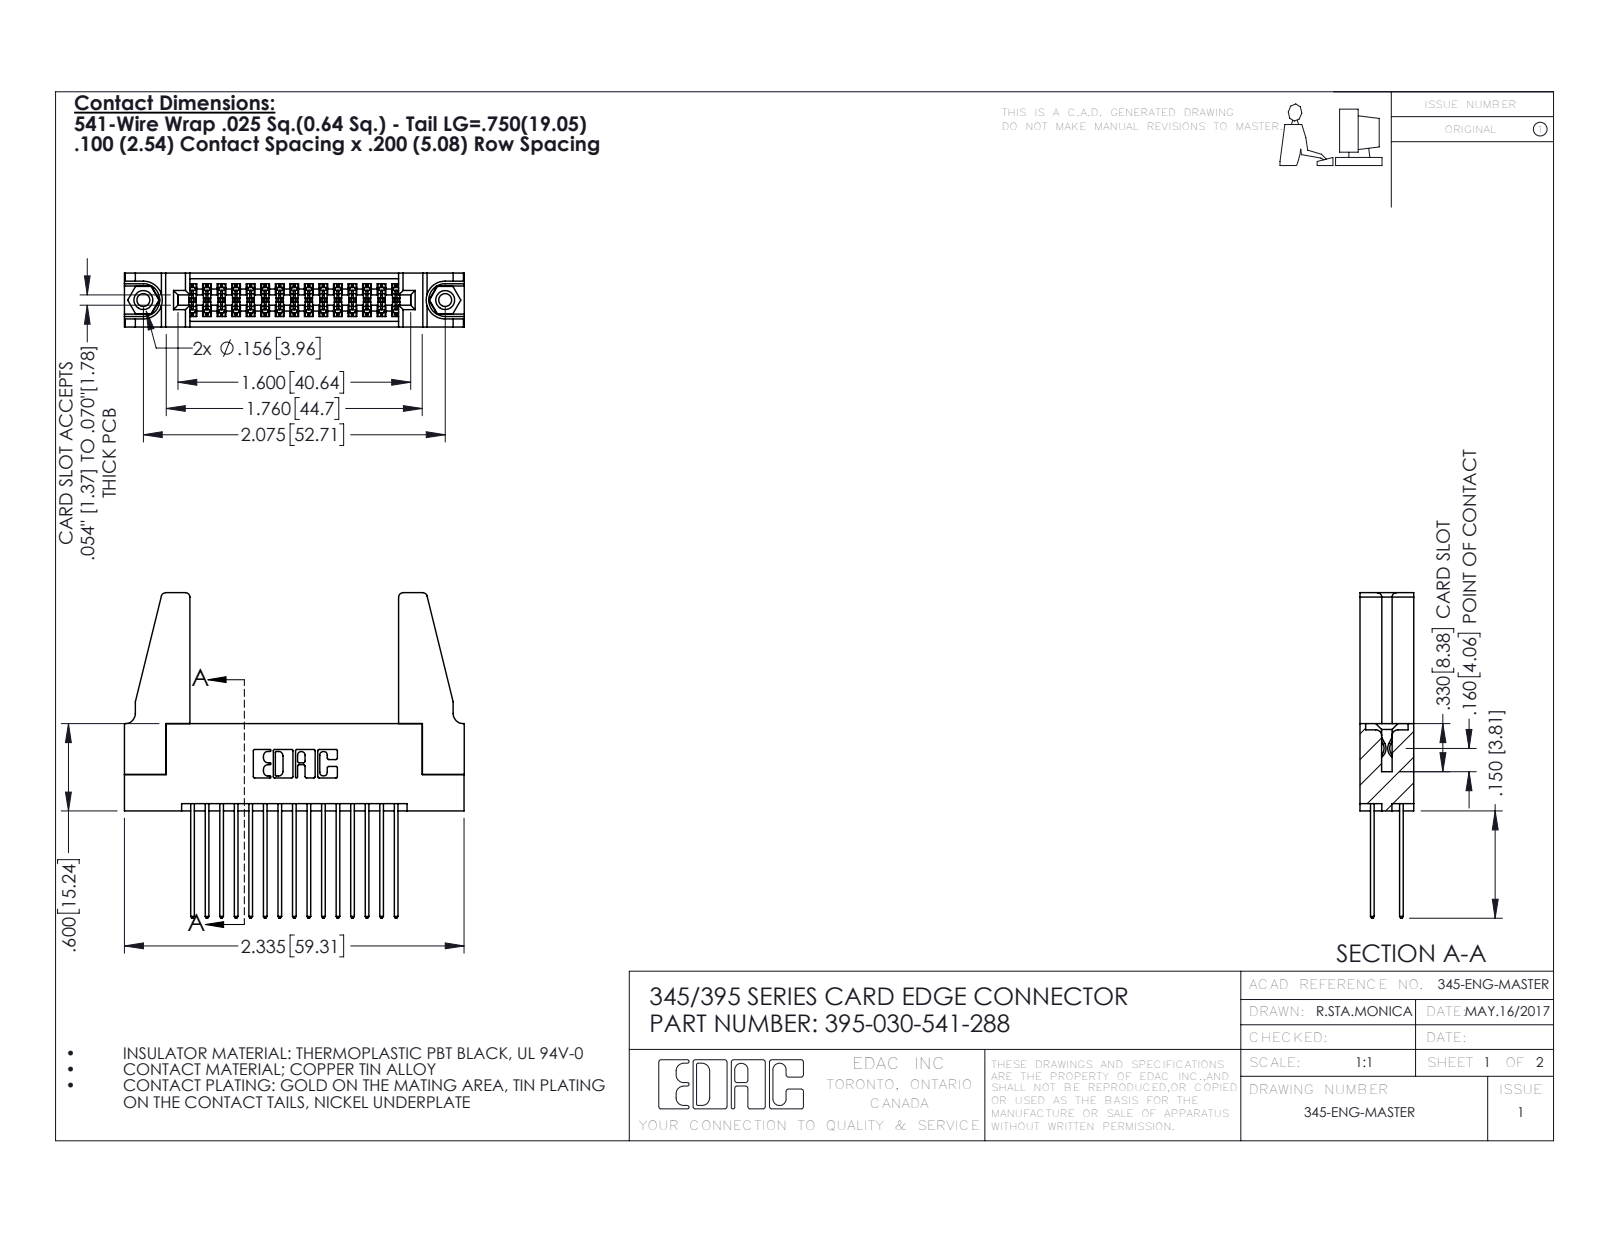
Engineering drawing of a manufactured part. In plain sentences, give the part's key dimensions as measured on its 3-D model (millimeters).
The part is named "395-030-541-288; 345-250-001_345-250-001-102; 345-220-078_345-220-088; 345-292-001_345-293-141 (+1 more)". Its 3-D file was written by "SolidWorks 2016 (CONFIG_CONTROL_DESIGN)". It is 35 solids with 1750 faces: 1142 planar, 592 cylindrical and 16 other. Overall it measures 59.3 by 56.8 by 9.4 millimeters. Its volume is 8 930 cubic millimeters and its surface area 11 810 square millimeters. Round holes: 2 of diameter 2.3, 2 of diameter 3.2, 2 of diameter 4, 1 of diameter 1.6. Round bosses or shafts: 2 of diameter 3.9. Partial cylindrical surfaces (rounded edges, fillets, slot ends): 45 of radius 0.2, 30 of radius 0.3, 22 of radius 0.3, 8 of radius 0.8, 6 of radius 0.2, 6 of radius 0.8, 3 of radius 0.7, 2 of radius 0.4. The main face-to-face distances are 1.8, 7.6, 5.1, 9.4, 2.5, 6.9, 0.6, 5.7, 4.4, 3.8. The hole center spacings are 6.9, 46.8, 52.7.
